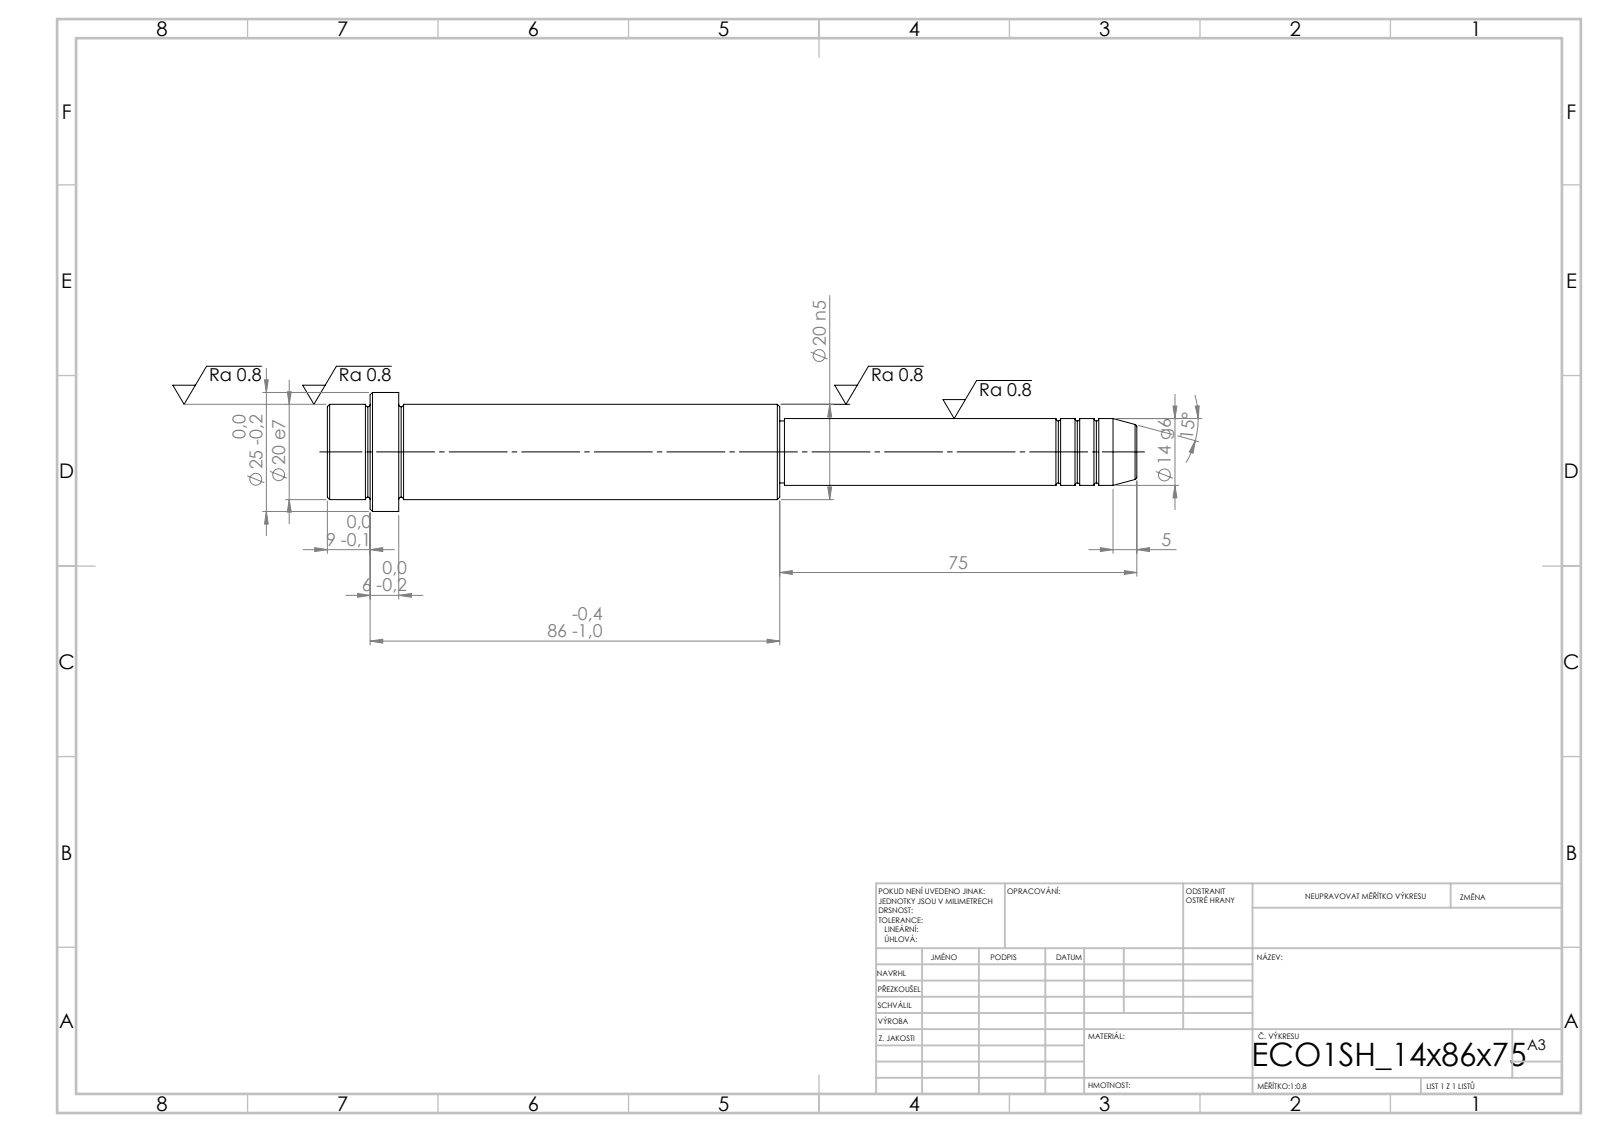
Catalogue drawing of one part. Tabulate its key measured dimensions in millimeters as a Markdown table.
| quantity | value |
| --- | --- |
| STEP written by | SolidWorks 2019 (CONFIG_CONTROL_DESIGN) |
| units | millimeters |
| bodies | 1 solid, 52 faces (6 planar, 16 cylindrical, 30 other) |
| overall size | 170 × 25 × 25 |
| volume | 42 167 mm³ |
| surface area | 10 382 mm² |
| round bosses / shafts (diameter × count) | 25 × 1, 20 × 1, 14 × 1, 13 × 1 |
| main face-to-face distances | 15, 80, 95, 86, 6, 9, 75, 155, 161, 170 |
